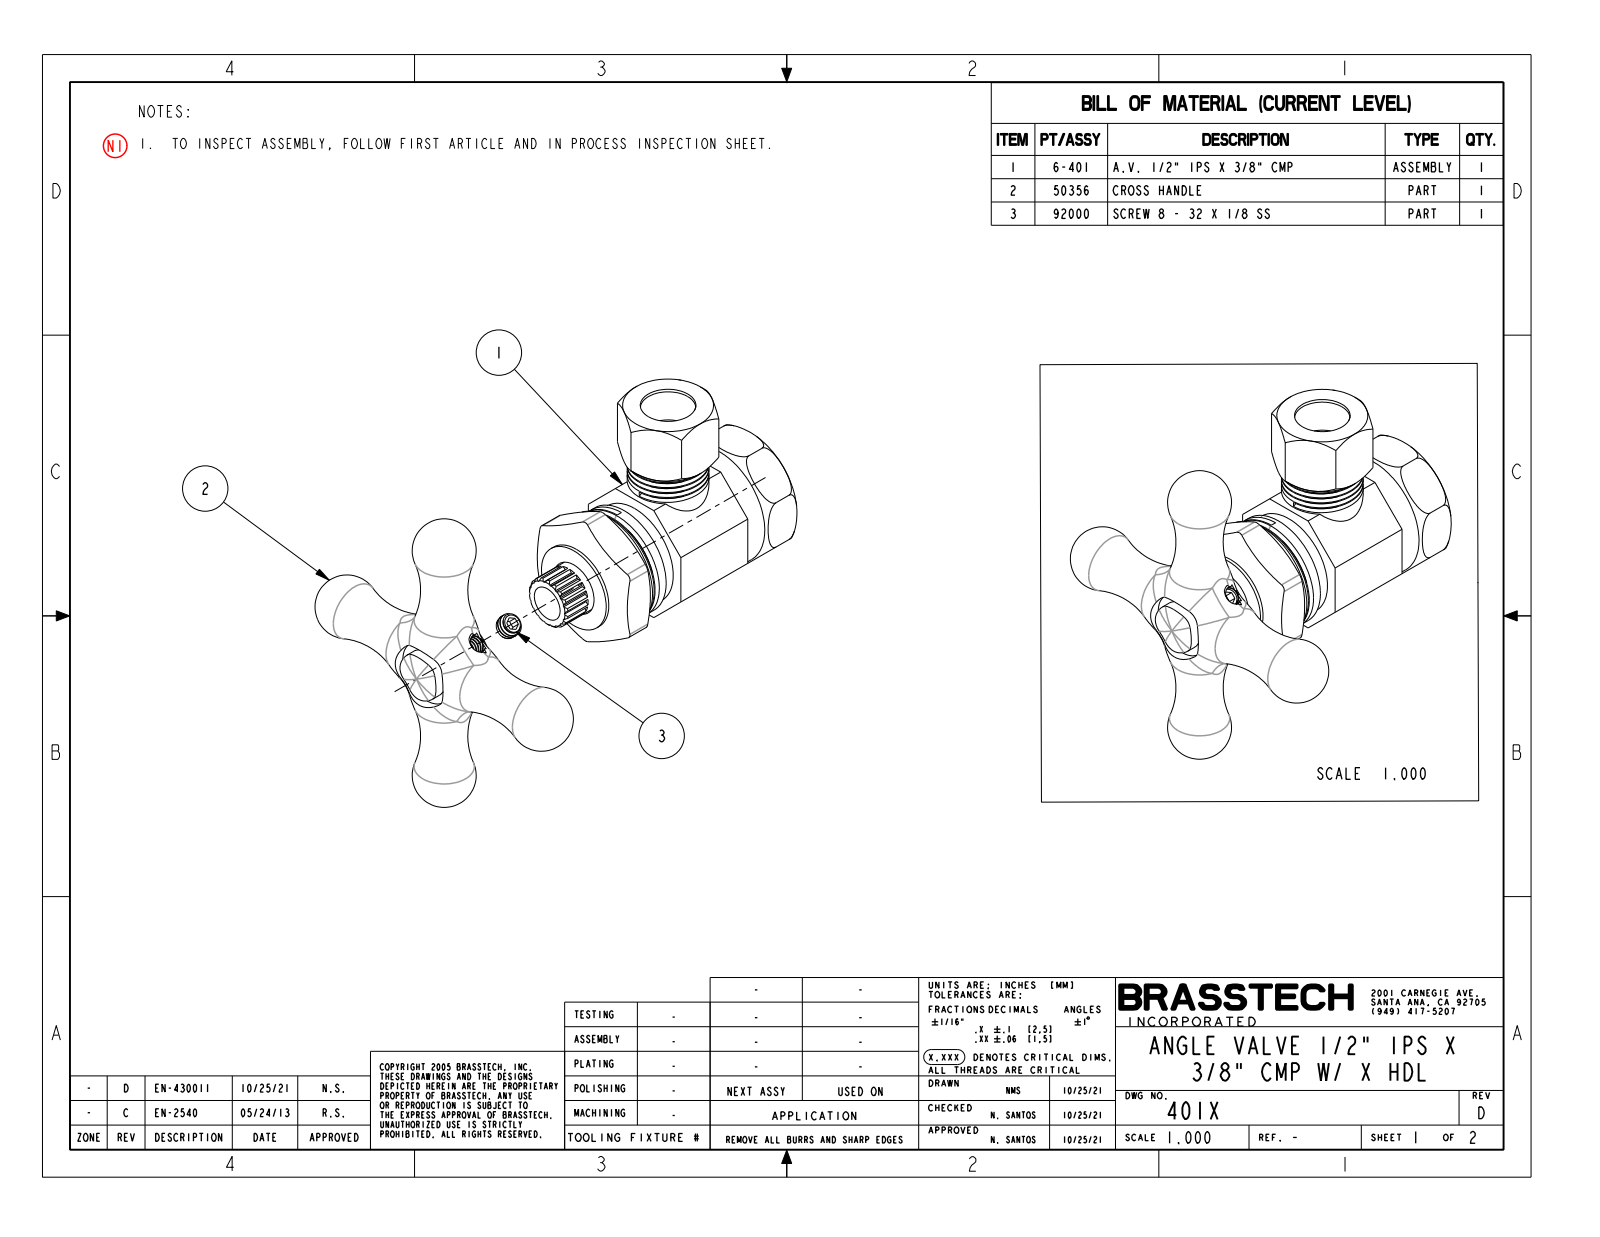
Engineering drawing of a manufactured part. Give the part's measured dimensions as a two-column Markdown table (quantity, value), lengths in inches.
| quantity | value |
| --- | --- |
| part name | 401X |
| STEP written by | CREO PARAMETRIC BY PTC INC, 2018500 (CONFIG_CONTROL_DESIGN) |
| units | inches |
| bodies | 2 solids, 753 faces (257 planar, 235 cylindrical, 261 other) |
| overall size | 2.33 × 2.33 × 2.288 |
| volume | 1.025 in³ |
| surface area | 35.05 in² |
| round holes (diameter × count) | 0.13 × 1, 0.375 × 1, 0.382 × 1, 0.392 × 1, 0.4 × 1, 0.464 × 1, 0.48 × 1, 0.517 × 1, 0.563 × 1, 0.75 × 1, 0.758 × 1, 0.813 × 1 |
| round bosses / shafts (diameter × count) | 0.86 × 1, 0.753 × 1, 0.68 × 1, 0.677 × 1, 0.629 × 1, 0.623 × 1, 0.62 × 1, 0.54 × 1 |
| partial cylindrical surfaces (radius × count) | 0.01 × 18, 0.05 × 6, 0.082 × 1, 0.17 × 1, 0.256 × 1, 0.376 × 1 |
| main face-to-face distances | 0.9, 0.625, 0.137, 0.763, 0.2, 1.531, 0.875, 0.575, 0.85, 0.65 |
